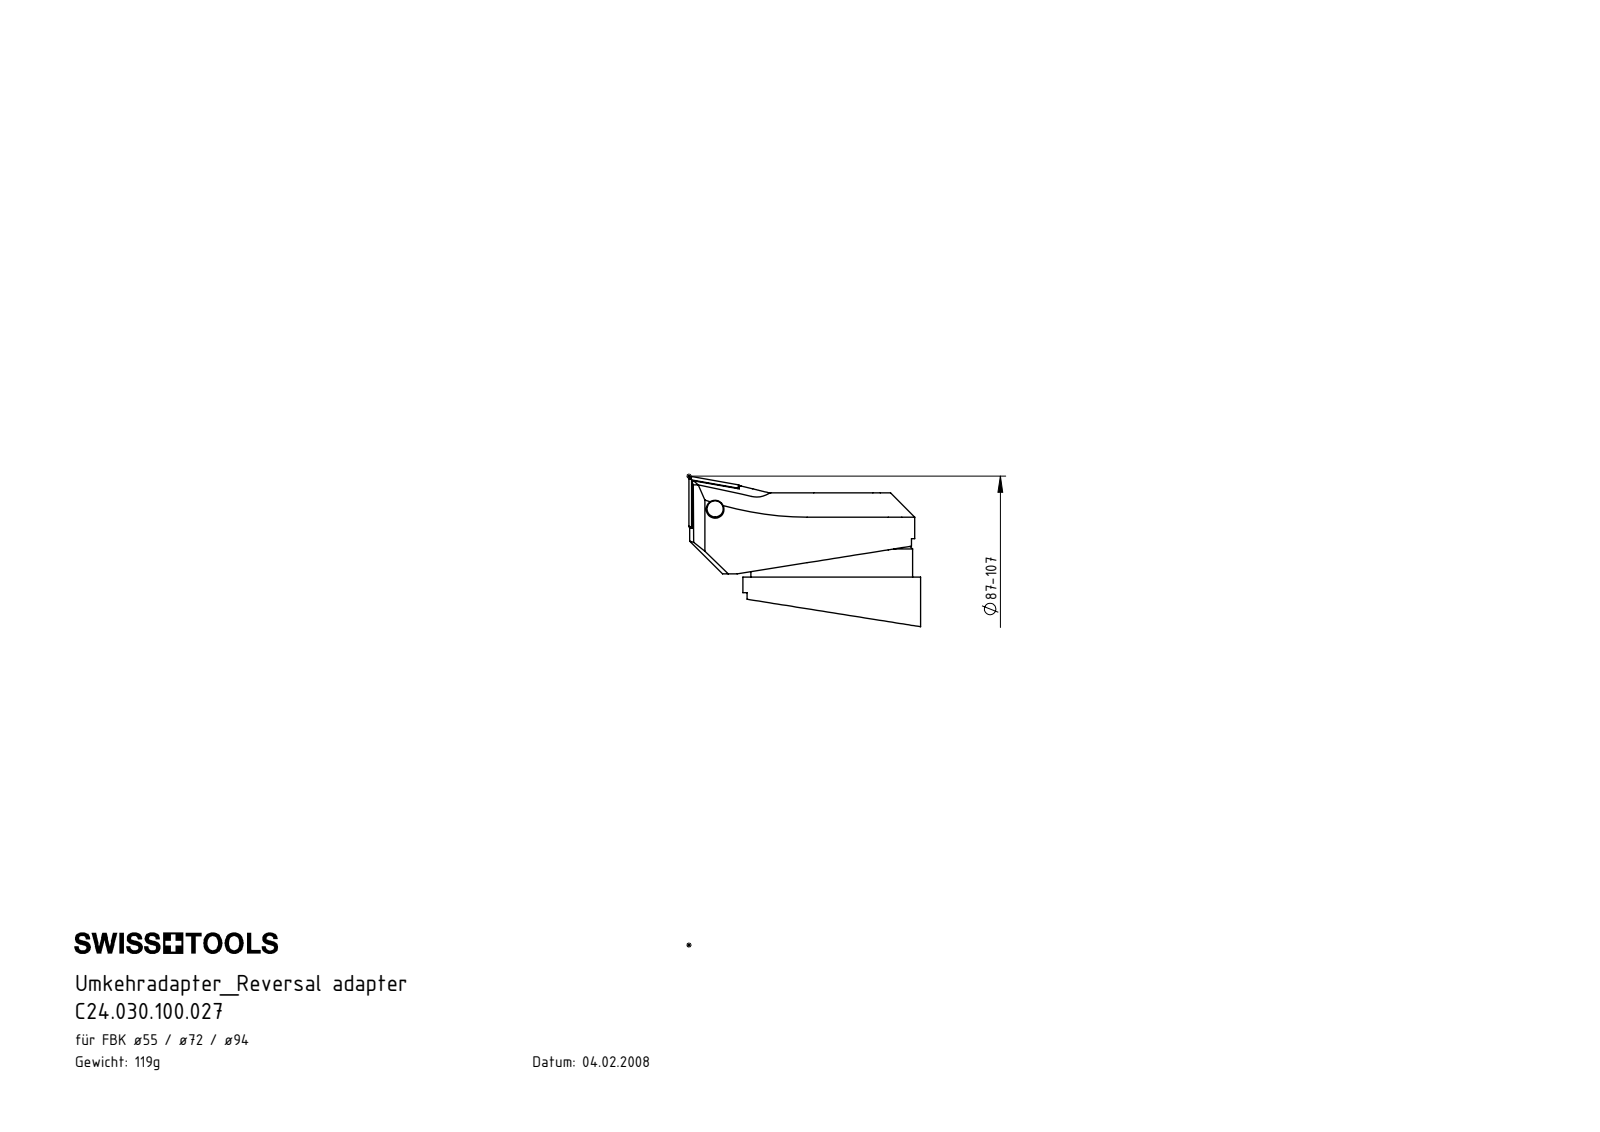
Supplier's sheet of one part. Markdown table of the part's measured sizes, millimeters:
| quantity | value |
| --- | --- |
| part name | F55-U00.001.010_B; C24.030.100.027 |
| STEP written by | SolidWorks 2017 (CONFIG_CONTROL_DESIGN) |
| units | millimeters |
| bodies | 1 solid, 29 faces (13 planar, 11 cylindrical, 5 other) |
| overall size | 33 × 33 × 15.53 |
| volume | 6 971 mm³ |
| surface area | 3 290 mm² |
| round holes (diameter × count) | 11 × 1, 30 × 1 |
| round bosses / shafts (diameter × count) | 33 × 1 |
| partial cylindrical surfaces (radius × count) | 0.5 × 2 |
| main face-to-face distances | 10, 5.6, 4.4, 8.5, 2.9, 1.5, 0.7, 6.3, 9.2, 10.7 |
